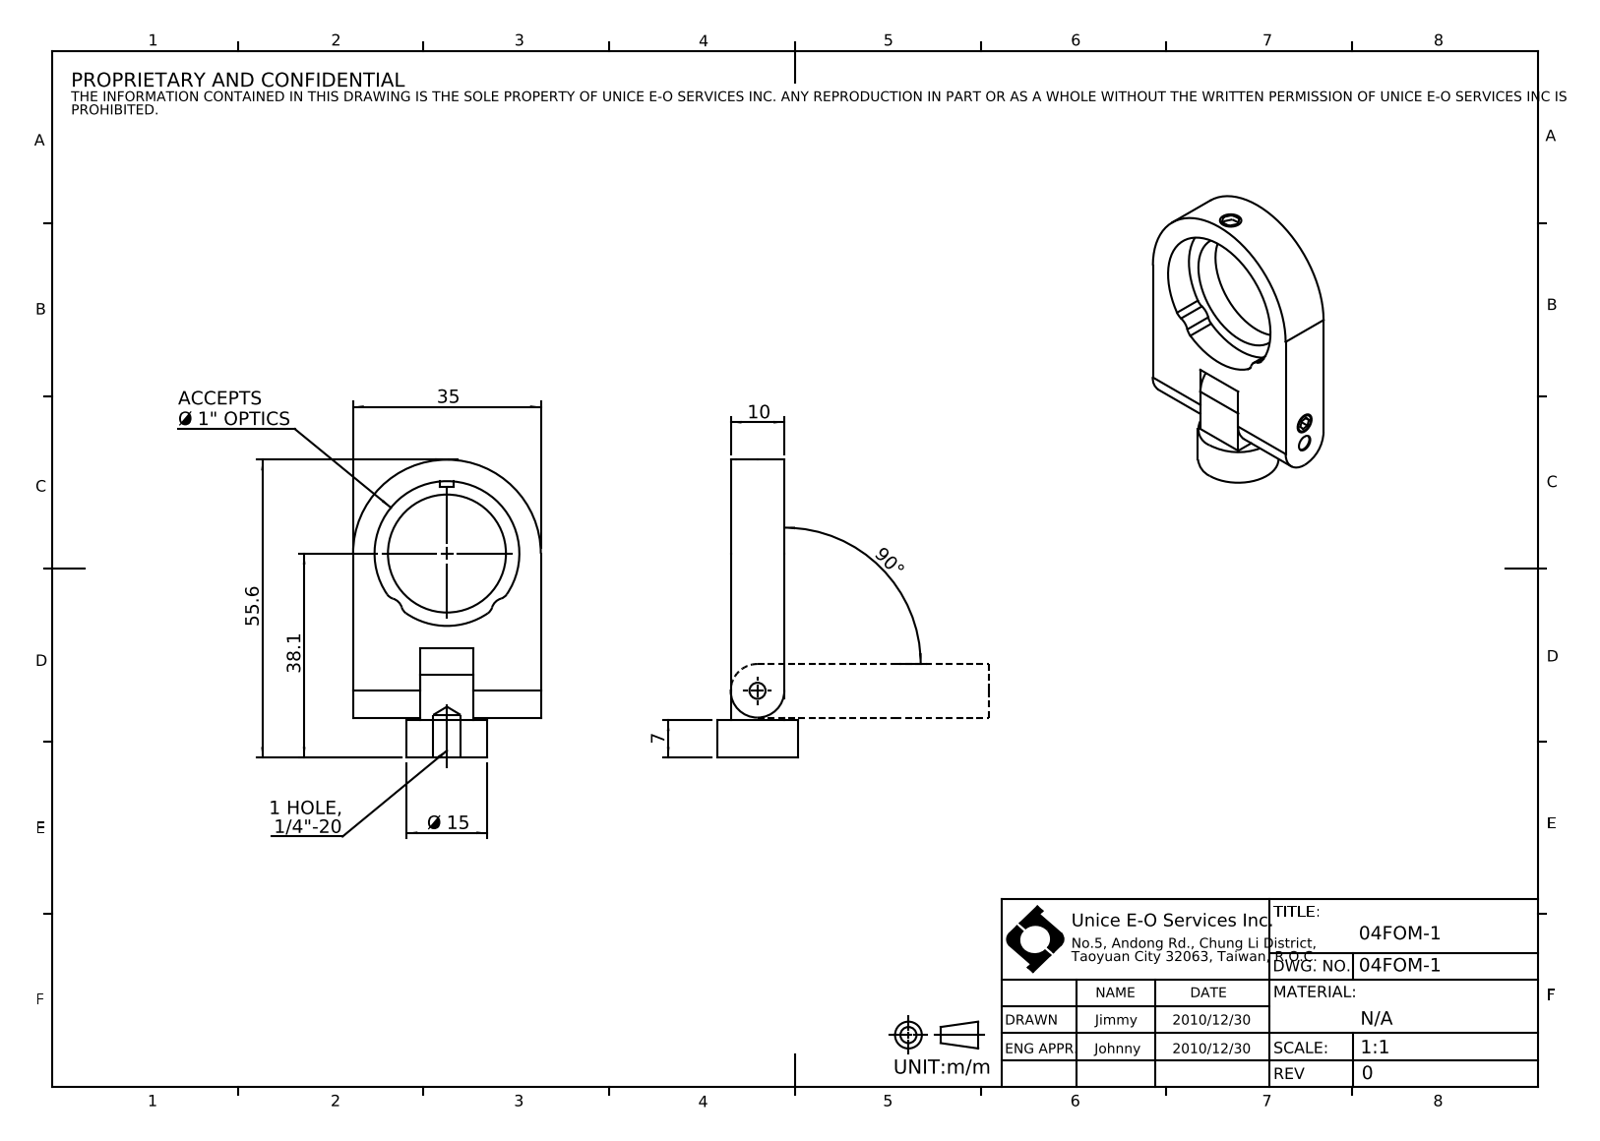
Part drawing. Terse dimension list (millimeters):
name: 04FOM-1
written by: SolidWorks 2016 (CONFIG_CONTROL_DESIGN)
unit: mm
bodies: 6 solids, 94 faces (37 planar, 42 cylindrical, 15 other)
size: 55.6 × 35 × 15
volume: 11 431 mm³; area: 6 810 mm²
holes: 2× ⌀3, 2× ⌀3.3, 1× ⌀5.11, 1× ⌀22, 1× ⌀27
bosses: 2× ⌀4, 1× ⌀15, 1× ⌀2.5
rounds: 4× R2, 2× R2.5, 2× R5, 1× R17.5
face distances: 10, 12.5, 22.5, 35, 5.5, 4.5, 20.5, 7, 13.5, 4
hole spacings: 2, 4.5
